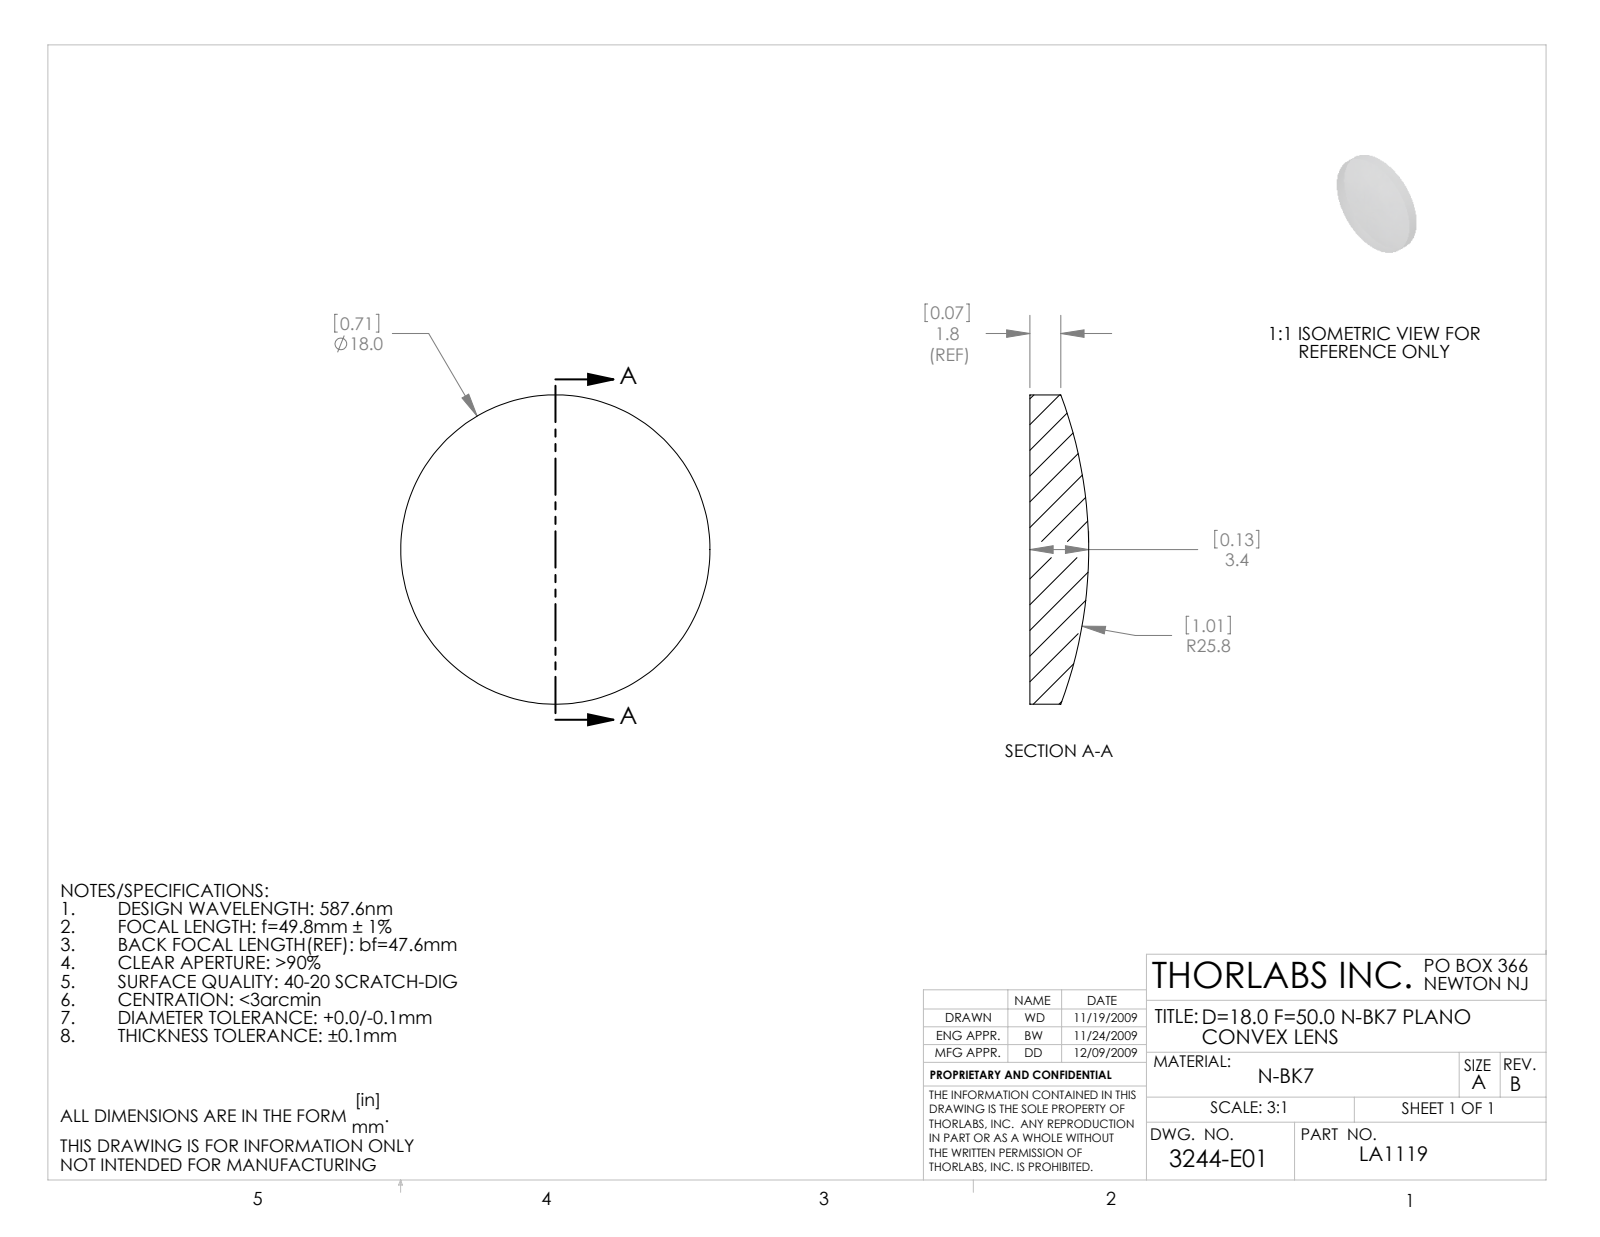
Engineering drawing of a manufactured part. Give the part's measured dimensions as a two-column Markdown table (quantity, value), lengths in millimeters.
| quantity | value |
| --- | --- |
| part name | 3244-E0W |
| STEP written by | SolidWorks 2009 (AUTOMOTIVE_DESIGN) |
| units | millimeters |
| bodies | 1 solid, 5 faces (1 planar, 2 cylindrical, 2 other) |
| overall size | 18 × 18 × 3.42 |
| volume | 666 mm³ |
| surface area | 619 mm² |
| round bosses / shafts (diameter × count) | 18 × 1 |
